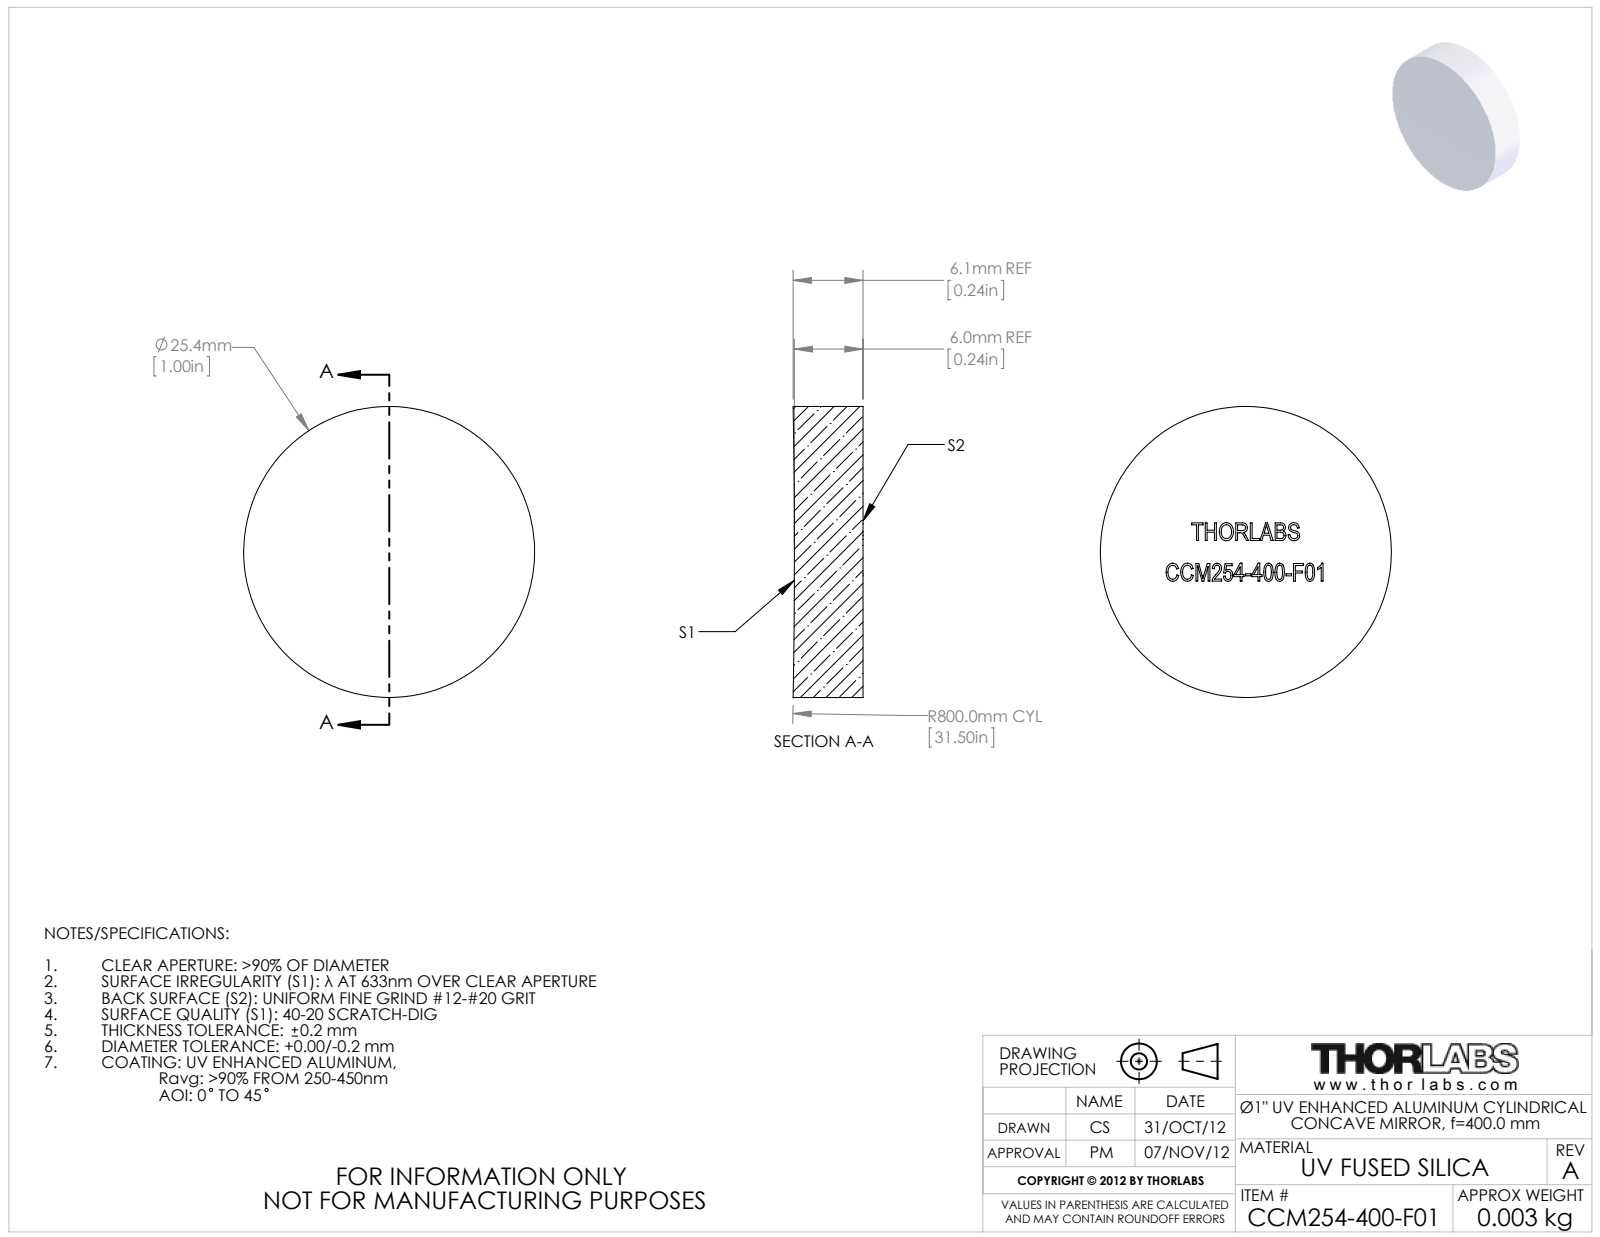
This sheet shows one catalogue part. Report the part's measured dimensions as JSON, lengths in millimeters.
{"part_name": "TTN005972-E0W", "step_written_by": "SolidWorks 2012 (CONFIG_CONTROL_DESIGN)", "units": "millimeters", "bodies": {"solids": 1, "faces": 37, "planar": 33, "cylindrical": 4, "other": 0}, "overall_size": [25.4, 25.4, 6.1], "volume_mm3": 3053, "surface_area_mm2": 1496, "round_bosses_or_shafts": [[25.4, 1]], "partial_cylinders_radius": [[800, 1]]}
